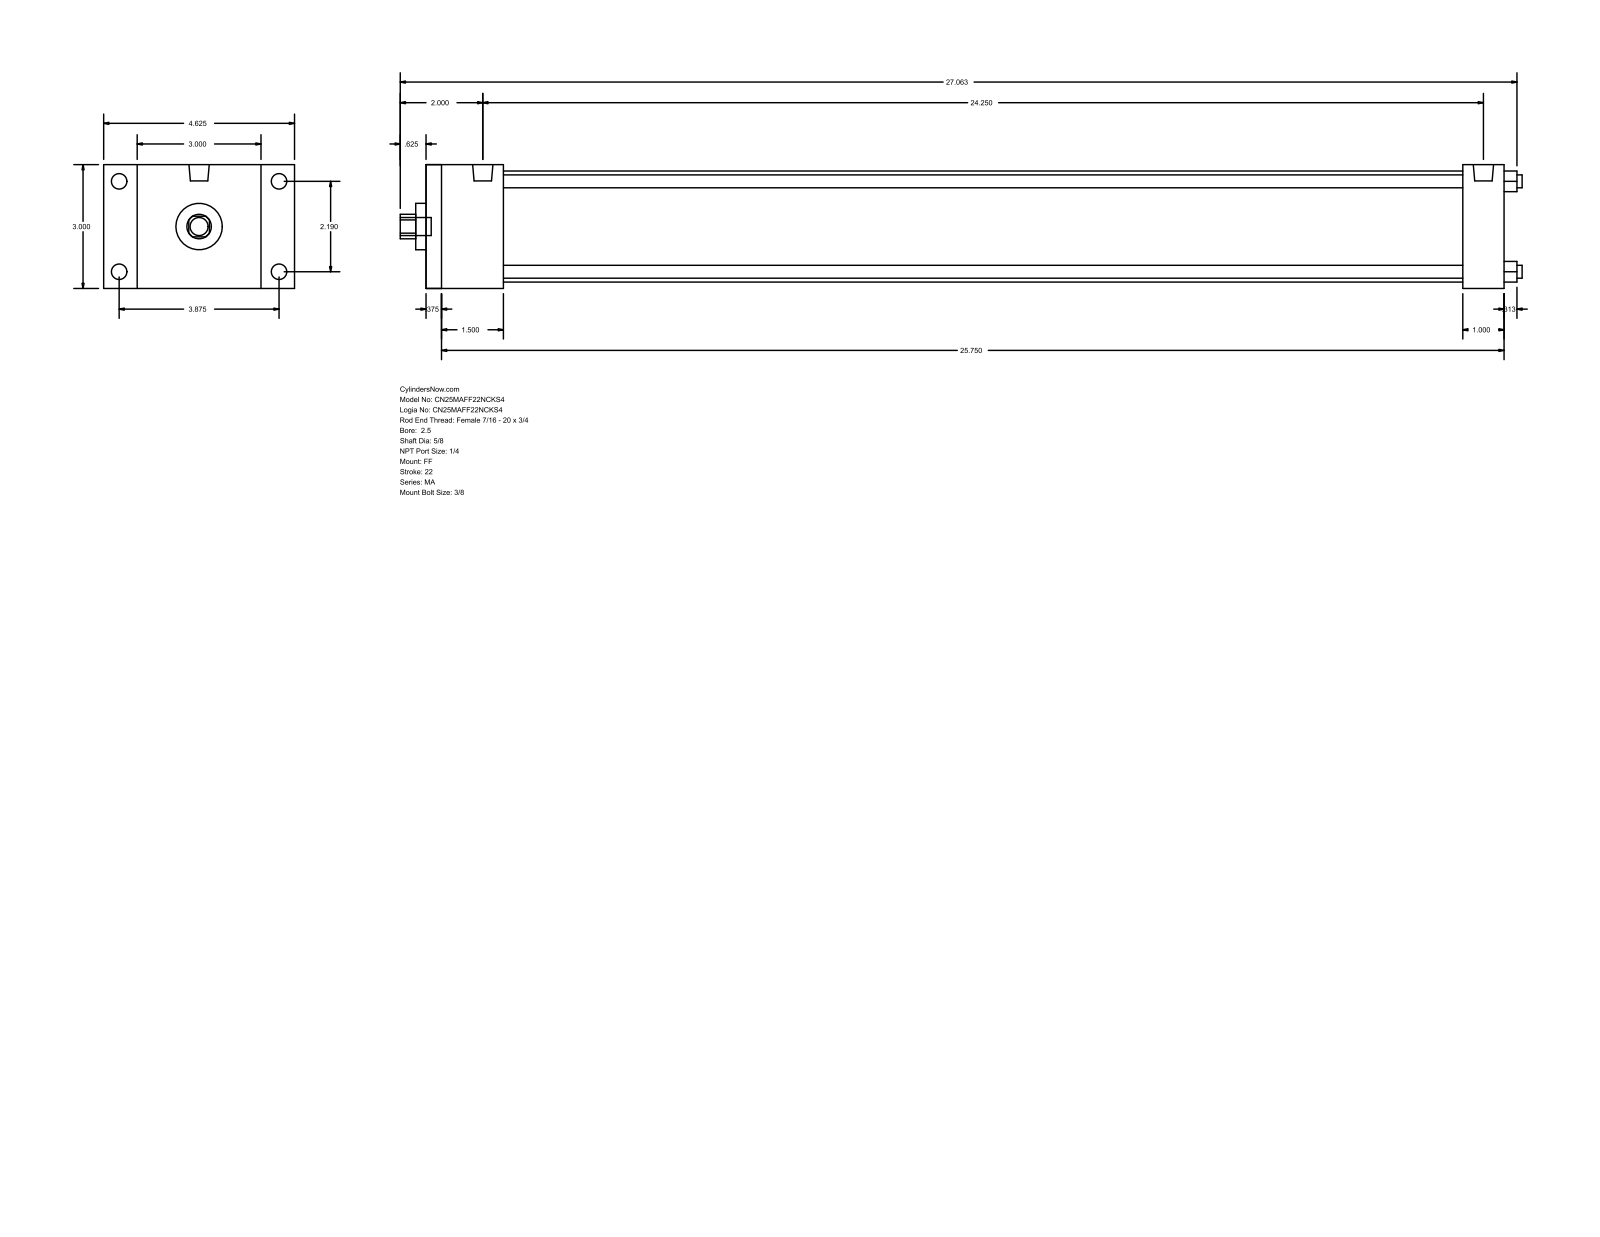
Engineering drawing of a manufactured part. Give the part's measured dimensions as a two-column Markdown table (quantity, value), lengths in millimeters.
| quantity | value |
| --- | --- |
| part name | MA_FF__0250_0.625 |
| STEP written by | GSSL Pune (CONFIG_CONTROL_DESIGN) |
| units | millimeters |
| bodies | 0 solids, 92 faces (64 planar, 28 cylindrical, 0 other) |
| overall size | 690.56 × 117.47 × 76.2 |
| round holes (diameter × count) | 7.94 × 4, 15.88 × 1, 28.57 × 1, 68.33 × 1 |
| round bosses / shafts (diameter × count) | 9.53 × 4, 7.94 × 4, 12.49 × 2, 11.11 × 1 |
| partial cylindrical surfaces (radius × count) | 7.54 × 1 |
| main face-to-face distances | 76.2, 663.57, 9.52, 654.05, 25.4, 47.62, 638.17, 38.1, 628.65, 590.55 |
| hole center spacings | 39.33, 55.62, 78.66 |
